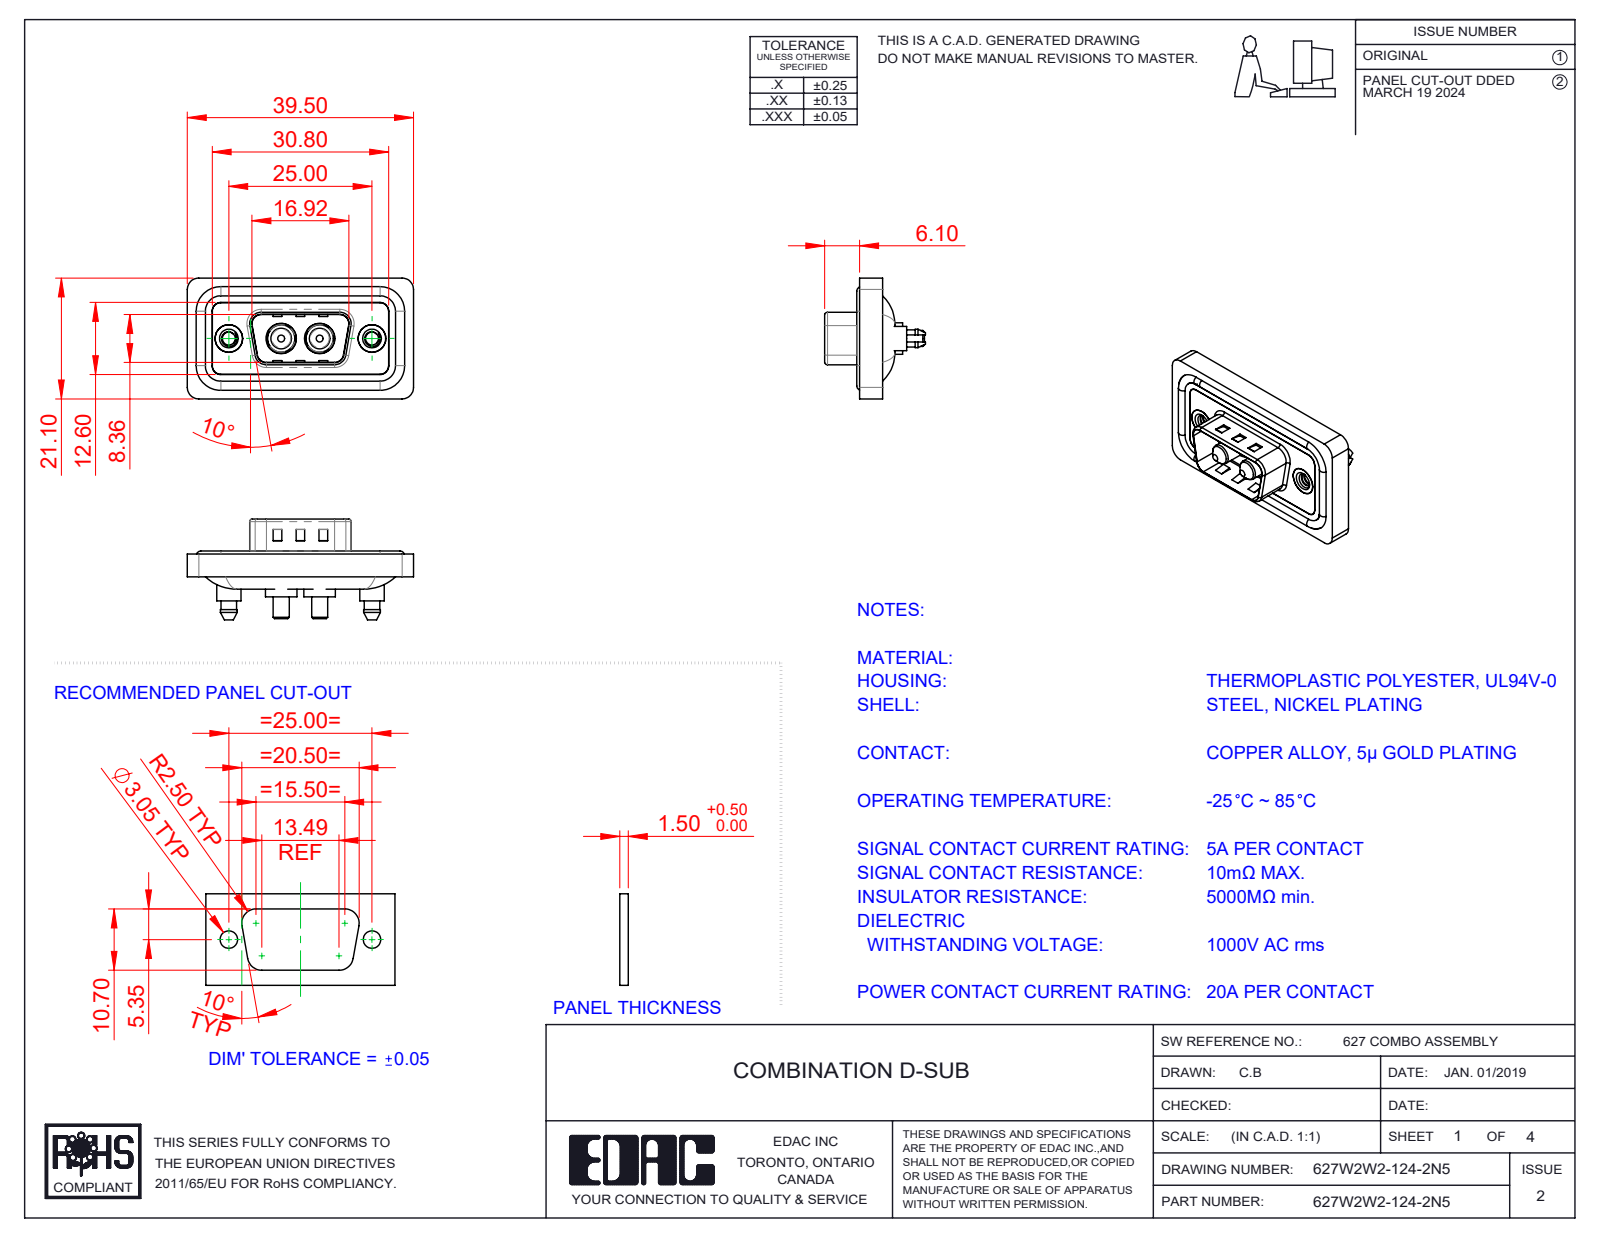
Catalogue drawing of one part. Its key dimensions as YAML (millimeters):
part_name: "627Combo Threaded Boardlock_5; 627Combo Housing_2W2; 627Combo Waterproof Housing_09 Contacts; 627Combo Shell Rear_09 Contacts (+3 more)"
step_written_by: "SolidWorks 2023 (CONFIG_CONTROL_DESIGN)"
units: millimeters
bodies: {solids: 11, faces: 539, planar: 181, cylindrical: 250, other: 108}
overall_size: [39.5, 21.1, 17.6]
volume: 4594
surface_area: 7317
round_holes:
  - {diameter: 2.26, count: 2}
  - {diameter: 4, count: 2}
  - {diameter: 4.8, count: 2}
  - {diameter: 4.85, count: 2}
  - {diameter: 5, count: 2}
  - {diameter: 5.3, count: 2}
round_bosses_or_shafts:
  - {diameter: 1.6, count: 4}
  - {diameter: 5.5, count: 2}
  - {diameter: 5.4, count: 2}
  - {diameter: 5.2, count: 2}
  - {diameter: 4.9, count: 2}
  - {diameter: 4.75, count: 2}
  - {diameter: 4.25, count: 2}
  - {diameter: 3.75, count: 2}
partial_cylinders:
  - {radius: 1.5, count: 24}
  - {radius: 2, count: 18}
  - {radius: 1.6, count: 10}
  - {radius: 0.5, count: 8}
  - {radius: 0.25, count: 4}
  - {radius: 0.6, count: 4}
  - {radius: 0.65, count: 4}
  - {radius: 0.9, count: 4}
face_to_face_distances: [0.4, 1.1, 2.9, 3.1, 0.5, 1.6, 1.5, 4, 0.7, 2.5]
hole_center_spacings: [9.14, 15.86, 6.72, 25]
